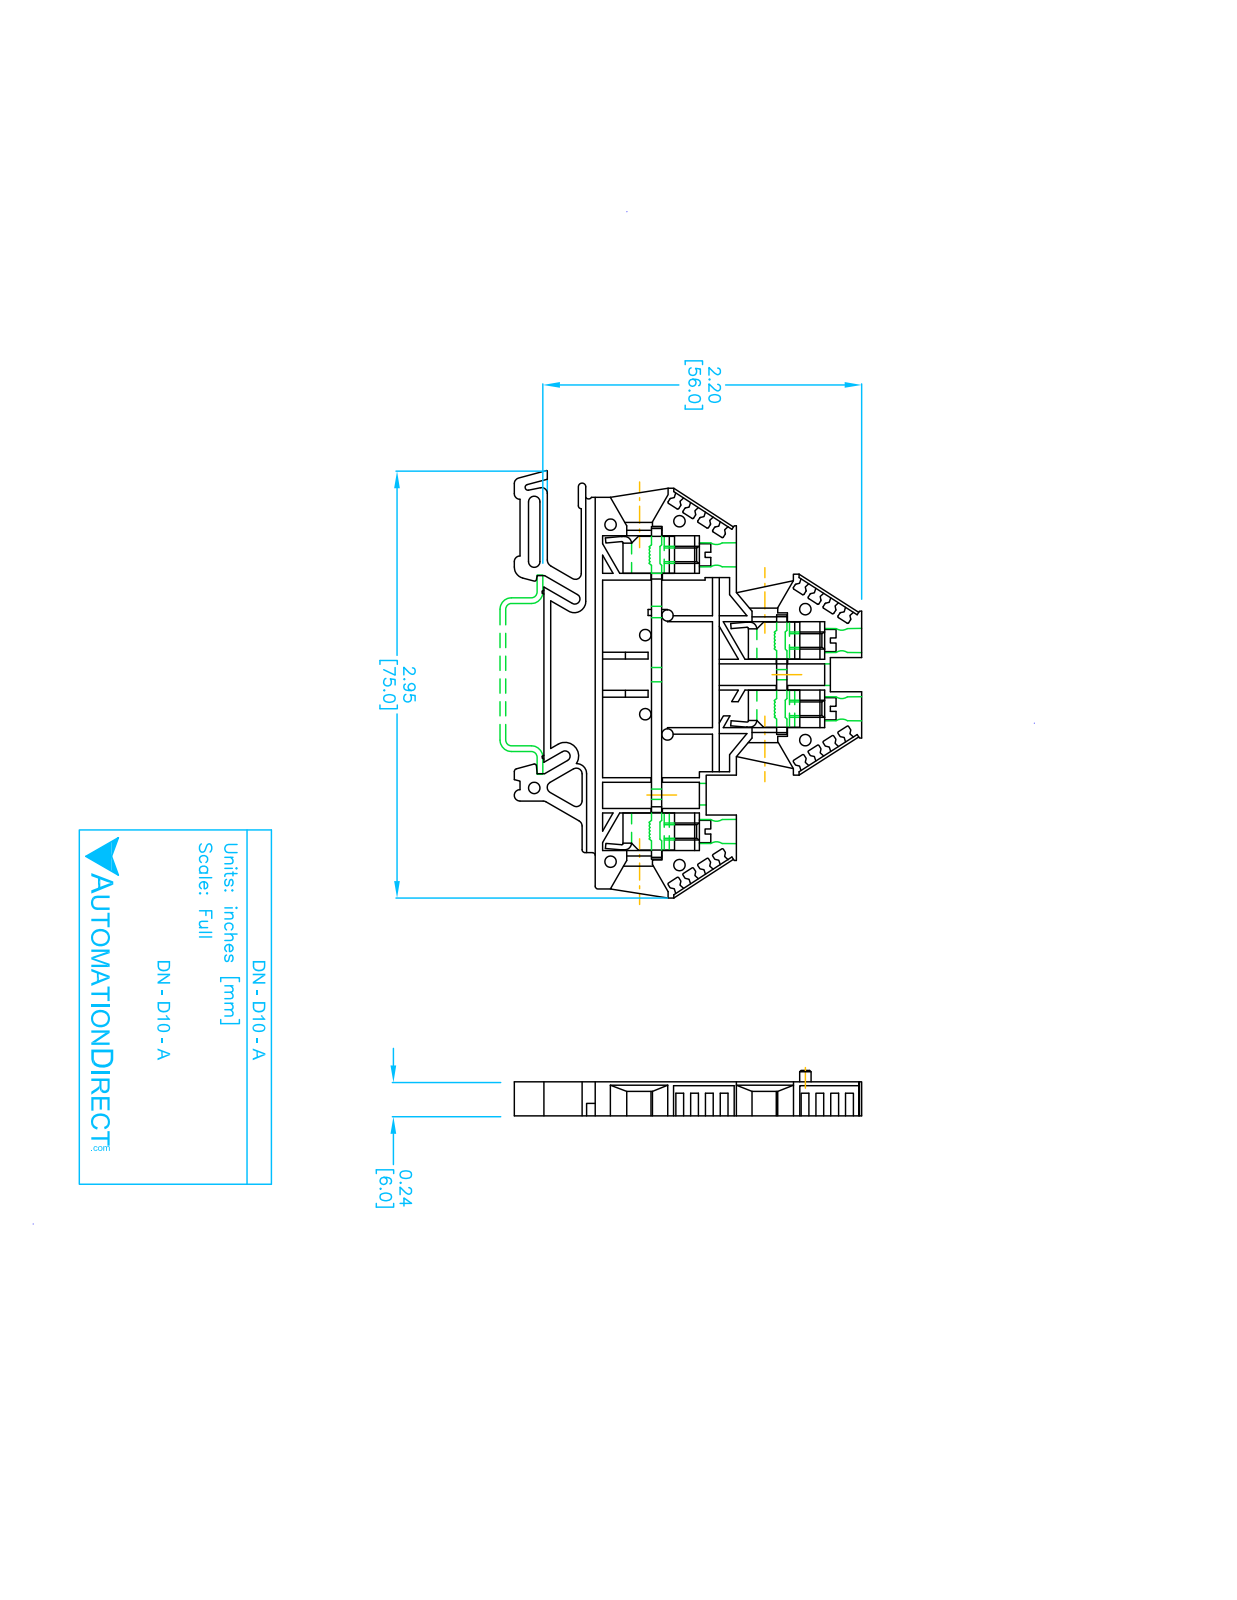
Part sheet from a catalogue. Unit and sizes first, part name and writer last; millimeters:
Units: millimetres
Overall size (bounding box): 75.1 × 61 × 6
Round holes (diameter × count): ⌀4.2 ×4, ⌀2 ×1
Round bosses / shafts (diameter × count): ⌀3.7 ×4
Partial cylindrical surfaces — rounded edges, fillets, slot ends (radius × count): R0.2 ×64, R1 ×13, R0.5 ×6, R0.3 ×2, R0.9 ×2, R1.9 ×2, R2 ×2, R0.1 ×1
Main face-to-face distances: 6, 2, 4, 9, 1.5, 0.6, 0.8, 1.2, 24.8, 1.8
Hole centre spacings: 12, 15.05, 21.55, 27.05, 33.55, 48.6
Volume: 14 742 mm³ · Surface area: 9 580 mm²
Bodies: 1 solid, 402 faces (261 planar, 141 cylindrical, 0 other)
Part name (STEP PRODUCT): 43550_DN-D10-A
STEP written by: SolidWorks 2013 (AUTOMOTIVE_DESIGN)
